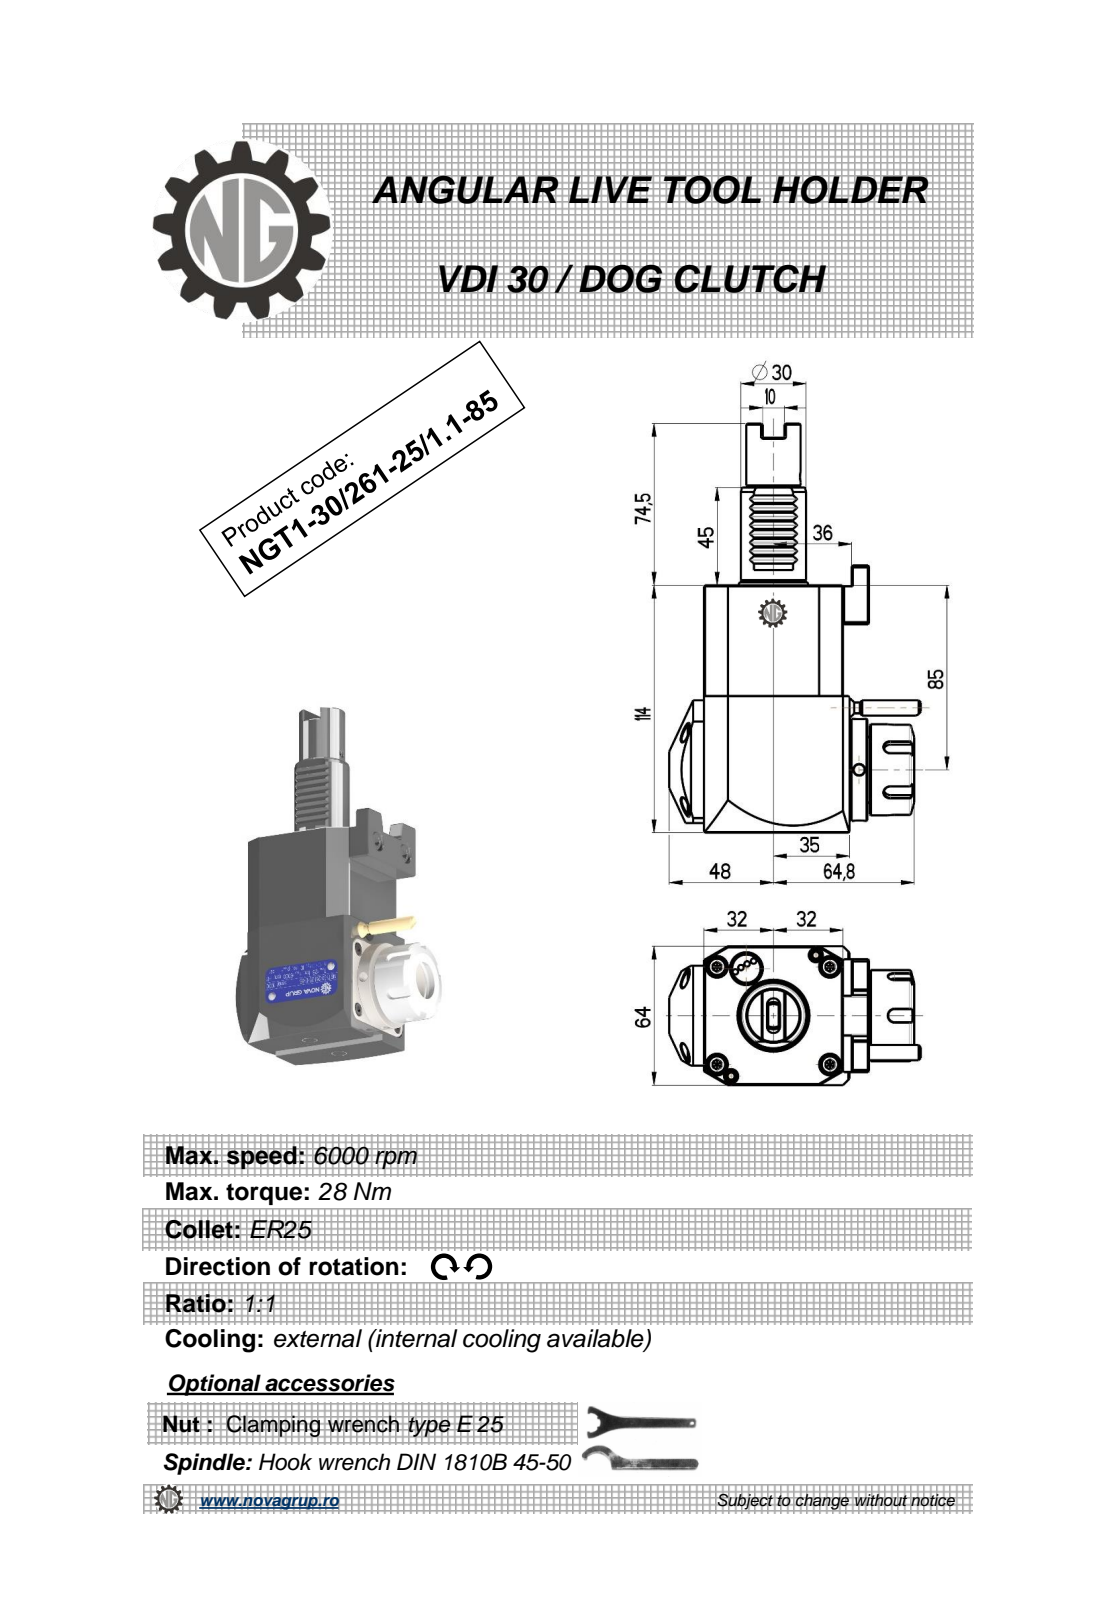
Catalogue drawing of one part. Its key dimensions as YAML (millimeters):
part_name: "NGT1_30_261_25_1_1_85"
step_written_by: "PRO/ENGINEER BY PARAMETRIC TECHNOLOGY CORPORATION, 2010280 (CONFIG_CONTROL_DESIGN)"
units: millimeters
bodies: {solids: 1, faces: 390, planar: 194, cylindrical: 64, other: 132}
overall_size: [188.5, 115.83, 64]
volume: 589551
surface_area: 56412
round_holes:
  - {diameter: 5, count: 2}
  - {diameter: 2.5, count: 1}
  - {diameter: 3, count: 1}
  - {diameter: 4.2, count: 1}
  - {diameter: 20.3, count: 1}
round_bosses_or_shafts:
  - {diameter: 47, count: 1}
  - {diameter: 42, count: 1}
  - {diameter: 35, count: 1}
  - {diameter: 30, count: 1}
  - {diameter: 25, count: 1}
  - {diameter: 8.96, count: 1}
  - {diameter: 7, count: 1}
  - {diameter: 5, count: 1}
partial_cylinders:
  - {radius: 0.3, count: 8}
  - {radius: 0.26, count: 6}
  - {radius: 3, count: 5}
  - {radius: 0.5, count: 2}
  - {radius: 1, count: 2}
  - {radius: 6, count: 2}
  - {radius: 160, count: 2}
  - {radius: 32, count: 1}
face_to_face_distances: [64, 114, 9, 3, 0.5, 67.2, 3.2, 67, 0.8, 8.8]
hole_center_spacings: [33.19, 107.85, 135]
